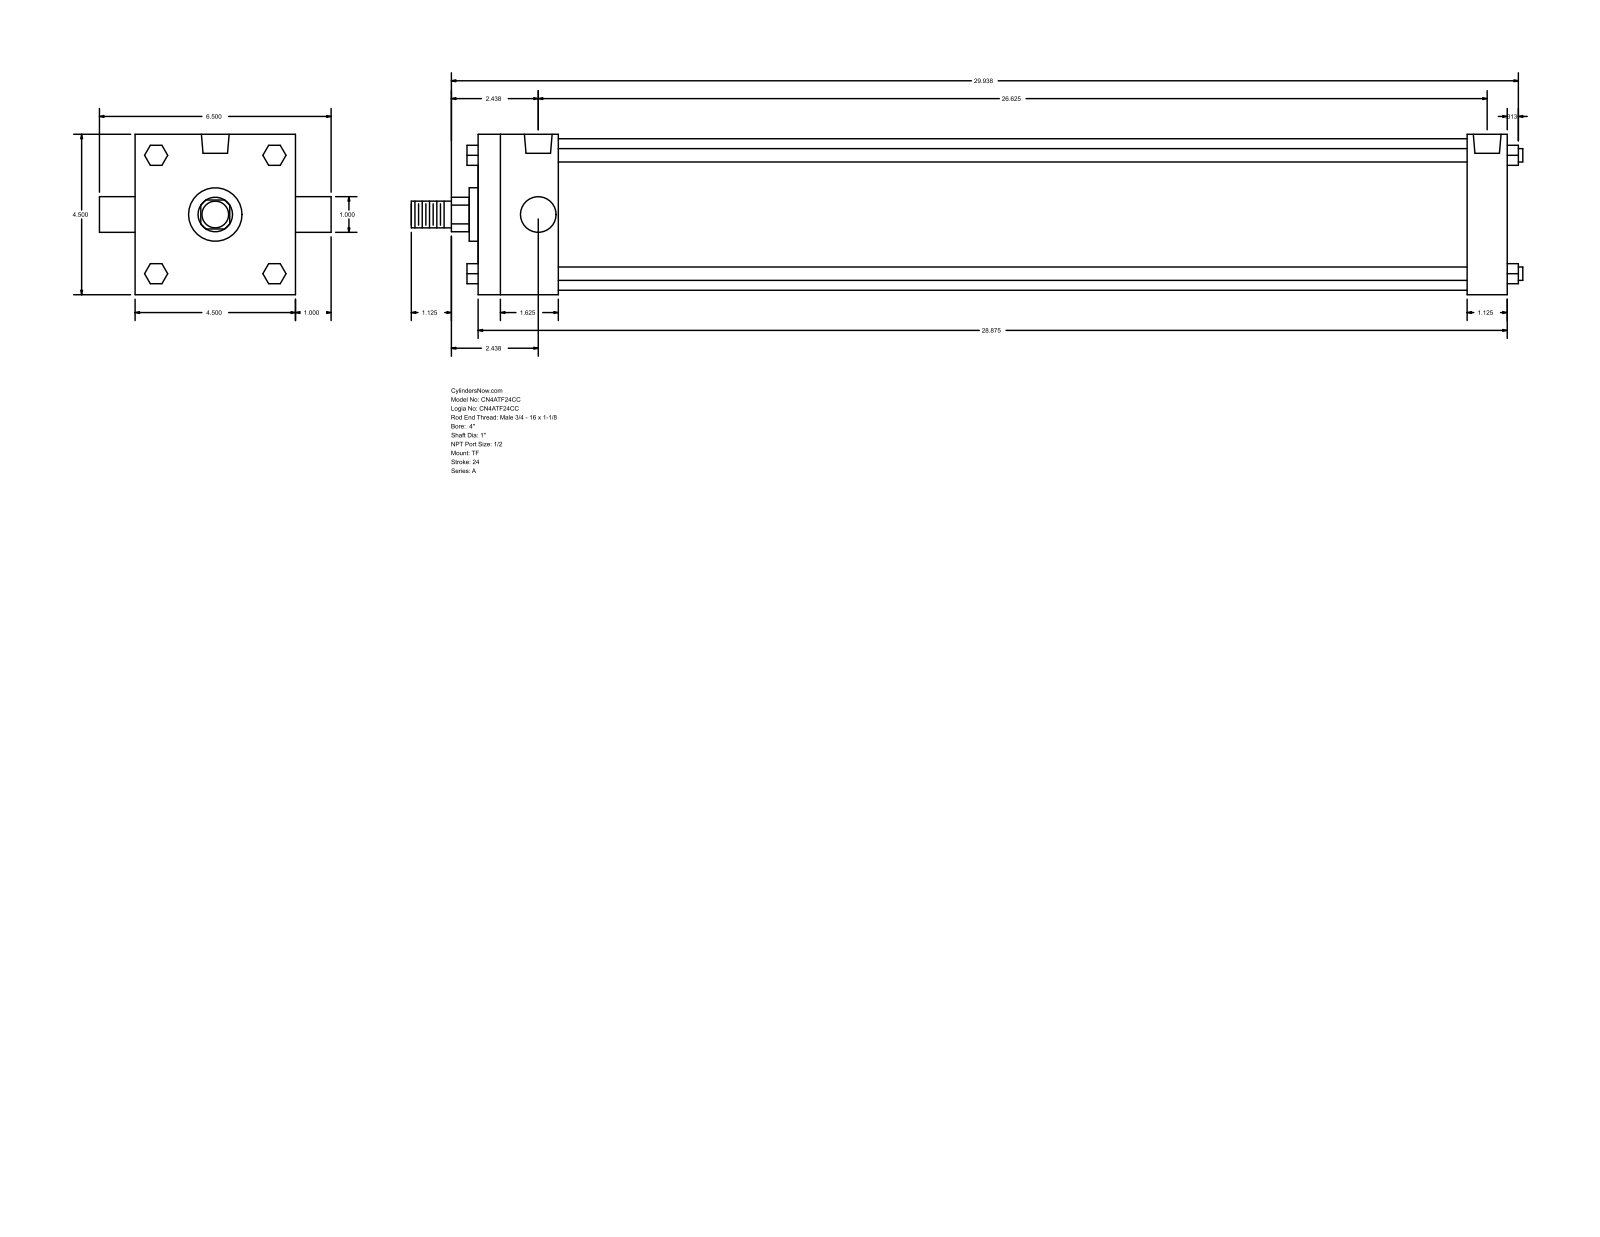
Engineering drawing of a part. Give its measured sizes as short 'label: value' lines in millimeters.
name: A_TF__0400_1
written by: GSSL Pune (CONFIG_CONTROL_DESIGN)
unit: mm
bodies: 0 solids, 120 faces (92 planar, 28 cylindrical, 0 other)
size: 792.16 × 165.1 × 114.3
holes: 3× ⌀8.73, 2× ⌀19.77
bosses: 4× ⌀9.53, 2× ⌀25.4, 1× ⌀107.95, 1× ⌀38.1, 1× ⌀19.05
rounds: 1× R12.29
face distances: 114.3, 733.43, 704.85, 28.58, 57.15, 647.7, 676.28, 14.29, 42.16, 73.03
hole spacings: 3.18, 673.1, 669.92, 676.28
